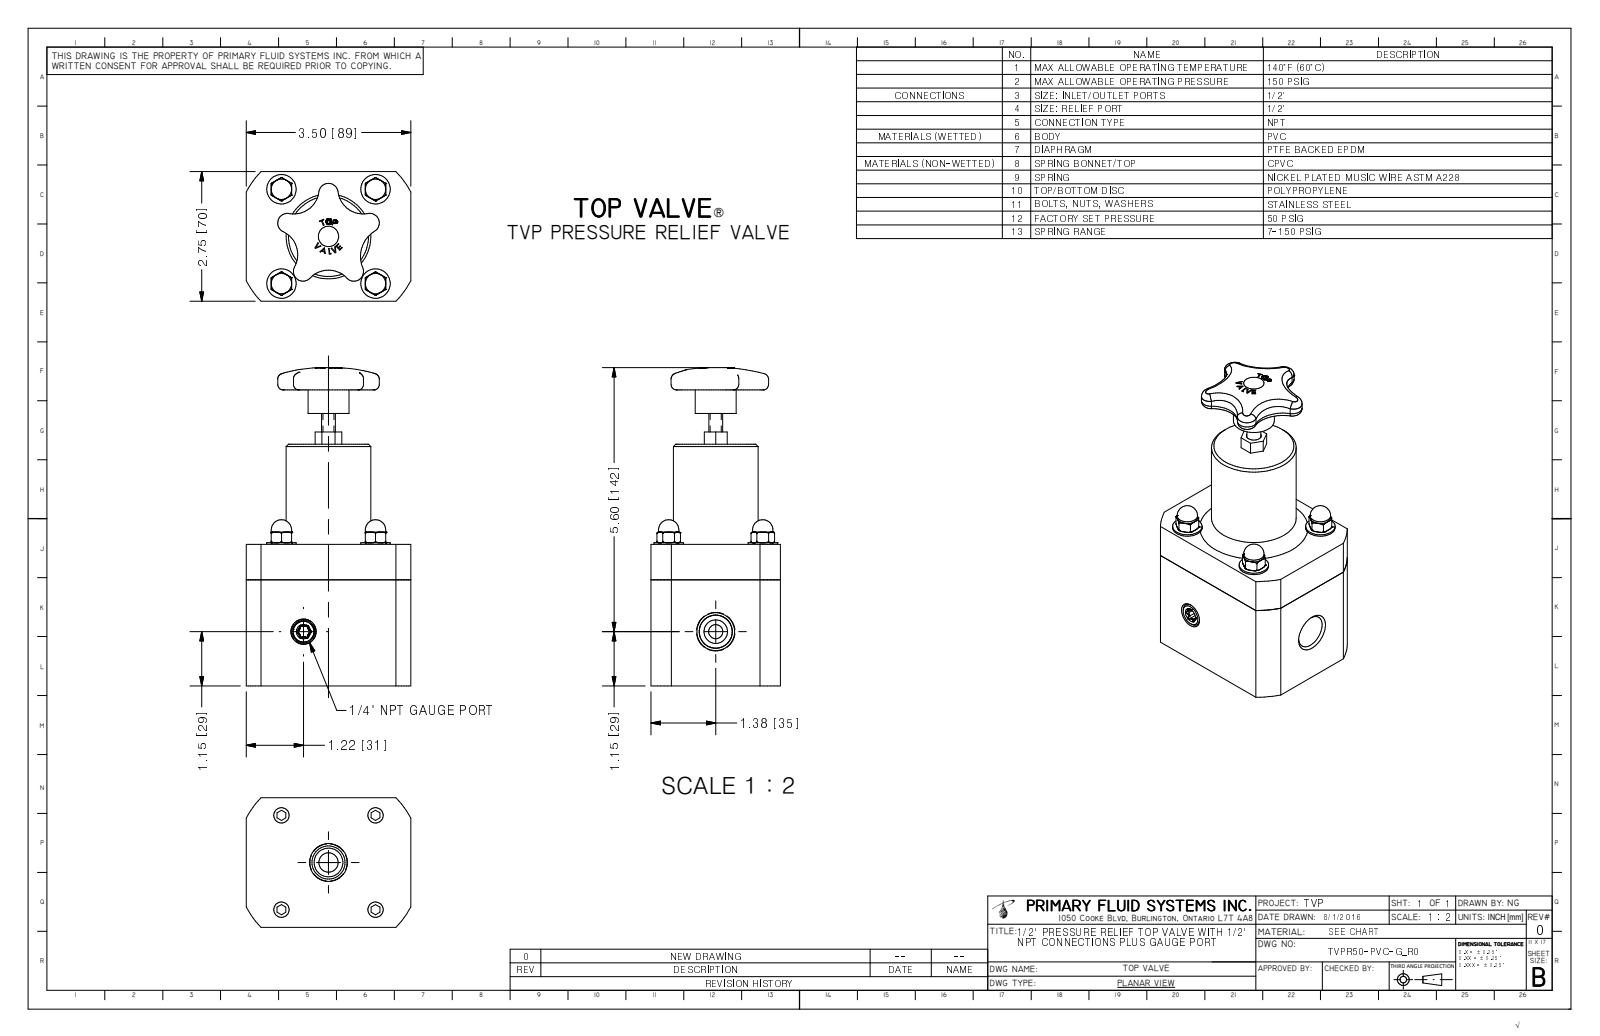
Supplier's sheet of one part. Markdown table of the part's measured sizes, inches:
| quantity | value |
| --- | --- |
| part name | TVPR50-PVC-G_R0 |
| STEP written by | Autodesk Inventor 2009 (AUTOMOTIVE_DESIGN) |
| units | inches |
| bodies | 1 solid, 339 faces (134 planar, 54 cylindrical, 151 other) |
| overall size | 6.75 × 3.5 × 2.75 |
| volume | 33.69 in³ |
| surface area | 92.3 in² |
| round holes (diameter × count) | 0.175 × 4, 0.703 × 2, 0.156 × 1, 0.437 × 1, 1.53 × 1, 2.4 × 1 |
| round bosses / shafts (diameter × count) | 0.625 × 4, 0.433 × 4, 2.375 × 1, 1.8 × 1, 0.87 × 1, 0.7 × 1, 0.293 × 1 |
| partial cylindrical surfaces (radius × count) | 0.027 × 6, 0.085 × 5, 0.205 × 5, 0.536 × 4, 0.656 × 4, 0.625 × 1, 0.745 × 1, 1.988 × 1 |
| main face-to-face distances | 2.75, 3.5, 3, 5.125, 2.125, 0.885, 2.115, 3.01, 3.25, 1.875 |
| hole center spacings | 1.414, 2, 2.828 |
